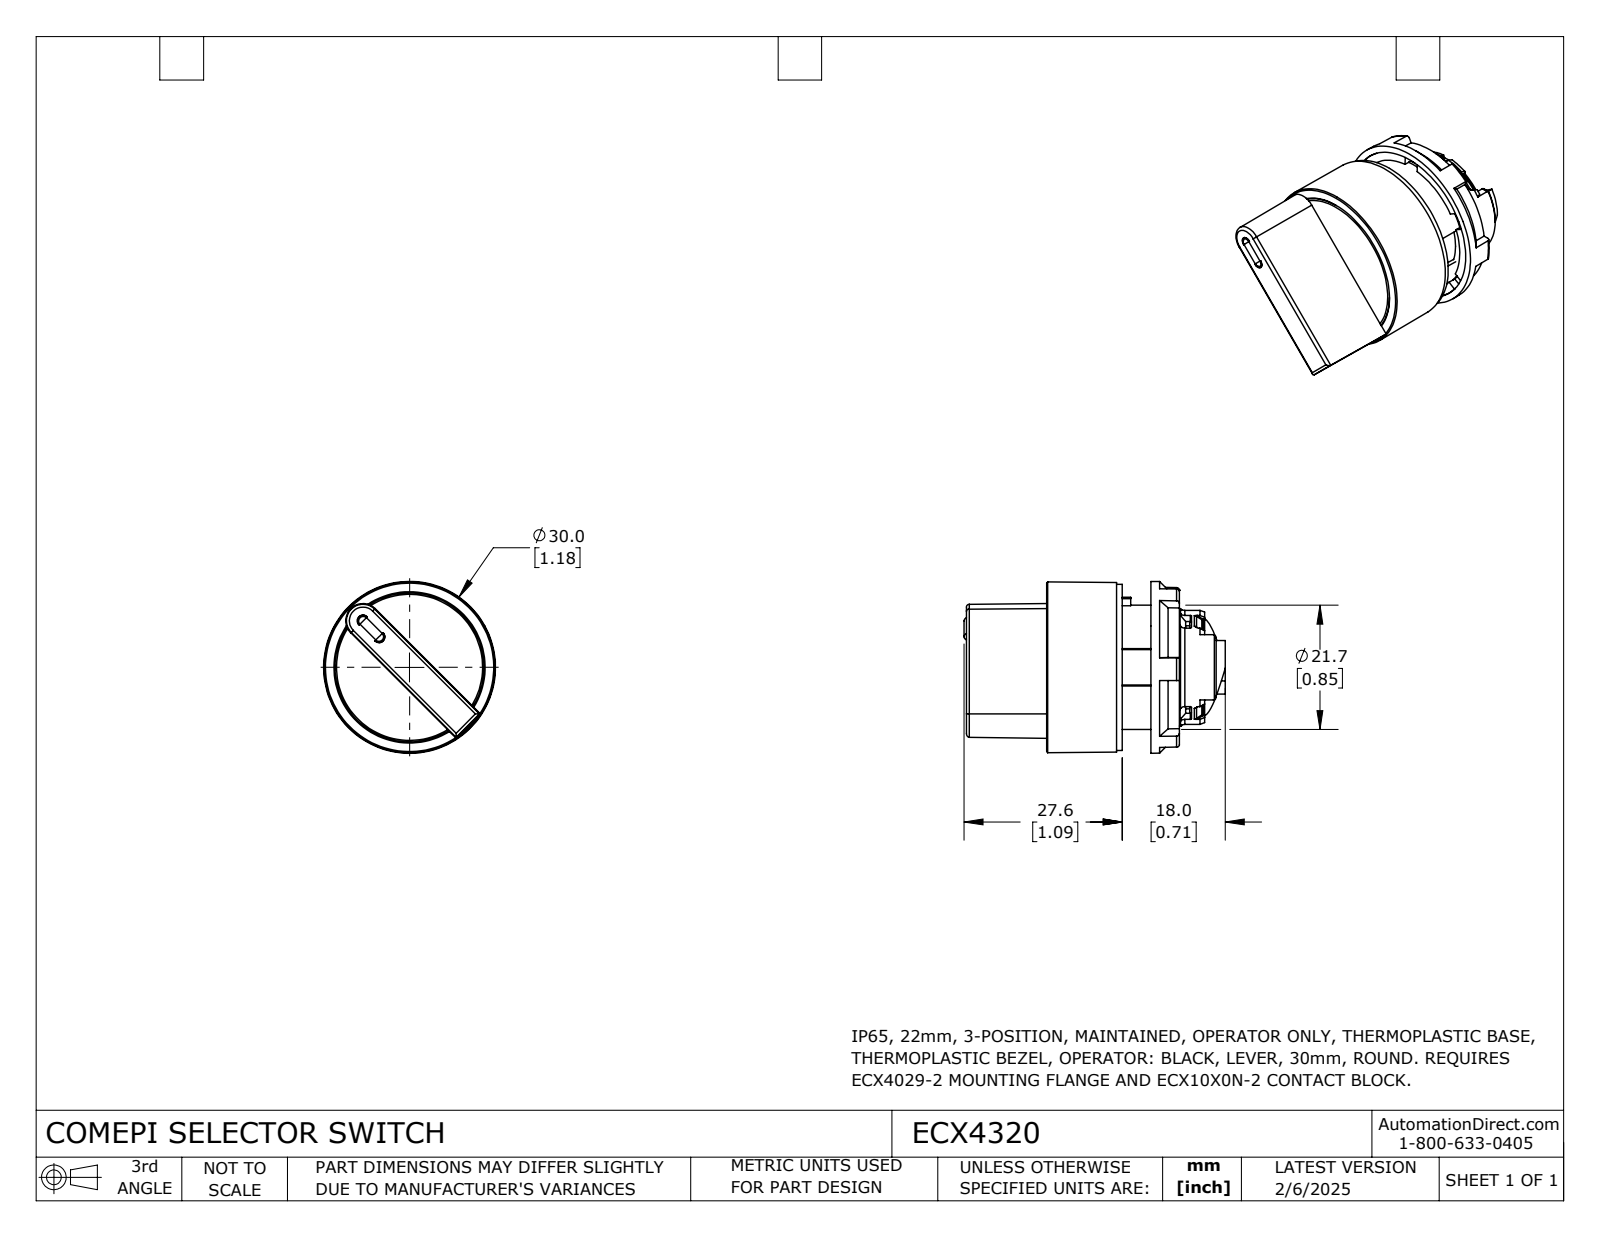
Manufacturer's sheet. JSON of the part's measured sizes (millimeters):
{"part_name": "ECX4320", "step_written_by": "SolidWorks 2024 (CONFIG_CONTROL_DESIGN)", "units": "millimeters", "bodies": {"solids": 3, "faces": 467, "planar": 175, "cylindrical": 145, "other": 147}, "overall_size": [45.6, 30, 30], "volume_mm3": 14400, "surface_area_mm2": 12730, "round_holes": [[2.5, 1], [3.3, 1], [6.2, 1], [8.8, 1], [12.7, 1], [14, 1], [18.1, 1], [19.1, 1], [20.6, 1], [21.7, 1], [24.8, 1], [26, 1]], "round_bosses_or_shafts": [[29, 1], [25.5, 1], [24.5, 1], [21.6, 1], [20.5, 1], [20, 1], [17.5, 1], [17.3, 1]], "partial_cylinders_radius": [[0.2, 24], [0.5, 7], [1, 5], [0.3, 2], [0.3, 2], [7.4, 1], [8.8, 1], [9.3, 1]], "face_to_face_distances": [12.2, 1, 10.7, 3, 6.1, 5, 23.2, 13.2, 2, 10.2]}
